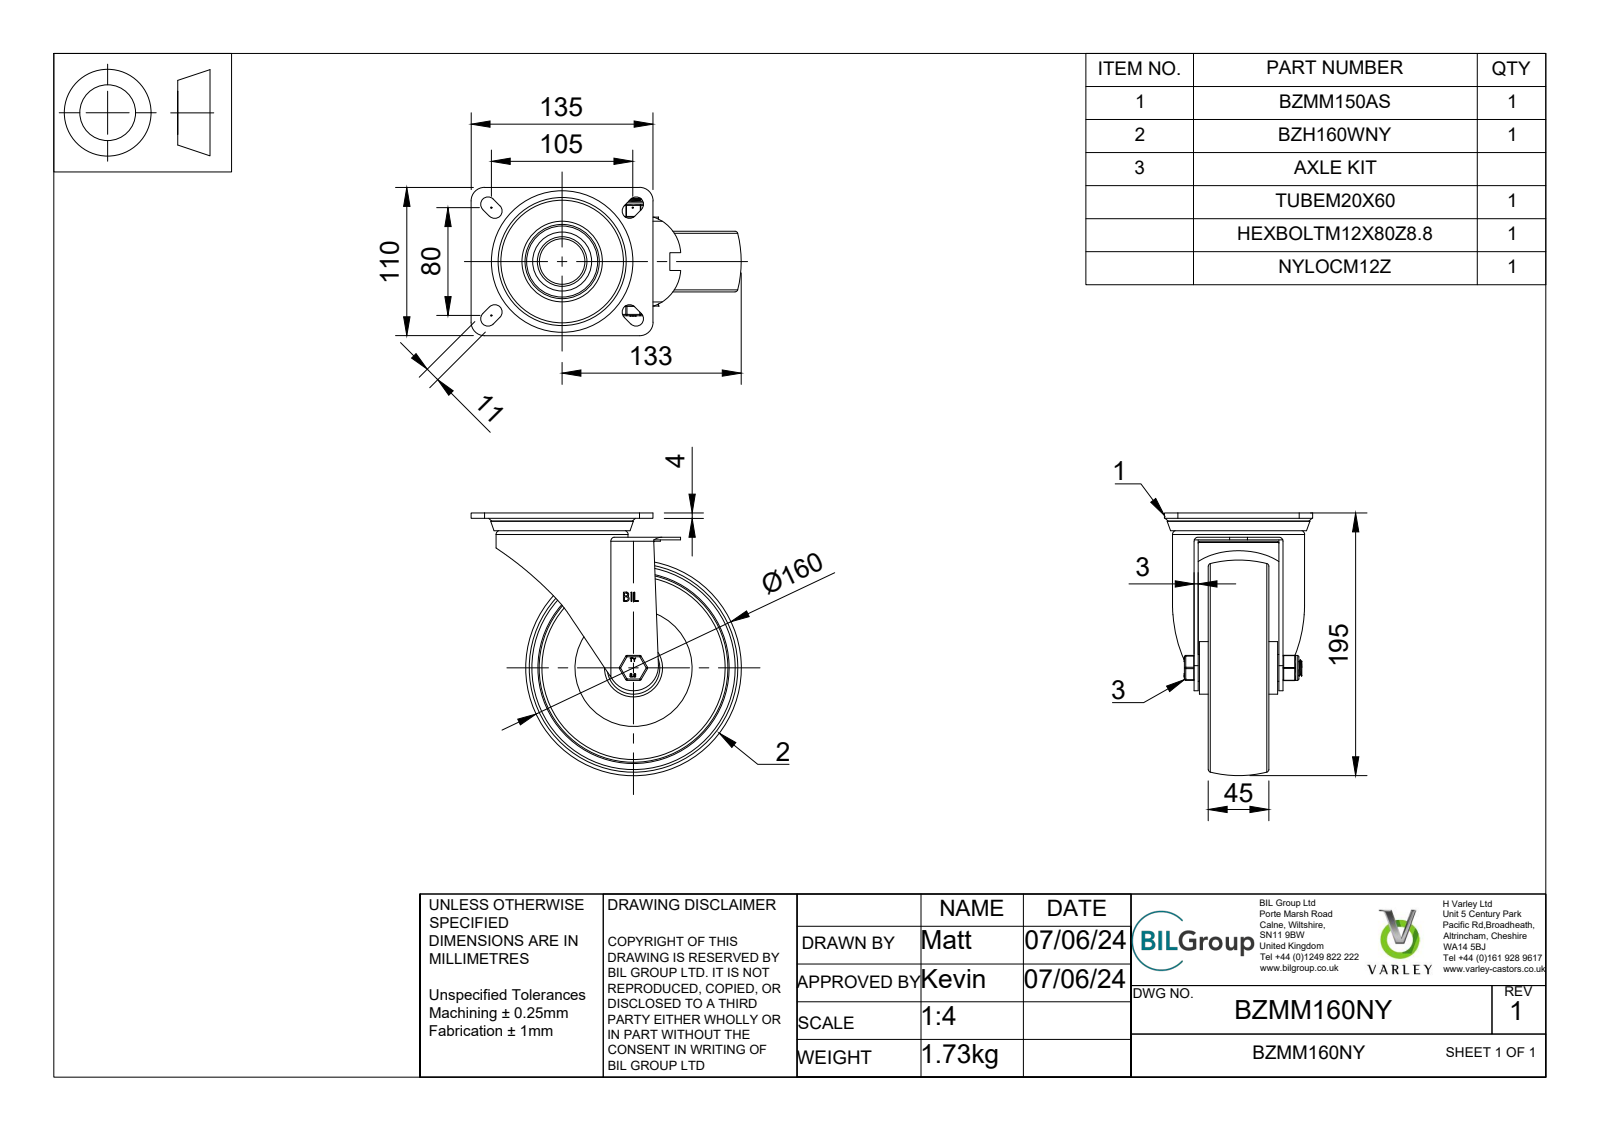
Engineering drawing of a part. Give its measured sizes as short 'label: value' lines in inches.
name: BZMM160NY v4; BZMM150AS - 2 v3; ZINC PLATED, PRESSED STEEL TOP PLATE; ZINC PLATED, PRESSED STEEL TOP PLATE Geometry (+7 more)
written by: Autodesk Translation Framework v13.14.0.145 (AUTOMOTIVE_DESIGN)
unit: in
bodies: 48 solids, 389 faces (127 planar, 119 cylindrical, 143 other)
size: 7.894 × 7.677 × 4.331
volume: 33.35 in³; area: 314.2 in²
holes: 1× ⌀0.472, 1× ⌀0.48, 1× ⌀0.492, 1× ⌀0.551, 1× ⌀0.807, 1× ⌀1.329, 1× ⌀1.565, 1× ⌀3.622, 1× ⌀5.512
bosses: 1× ⌀3.858, 1× ⌀3.071, 1× ⌀1.969, 1× ⌀1.535, 1× ⌀0.783, 1× ⌀0.728, 1× ⌀0.709, 1× ⌀0.466
rounds: 18× R0.02, 12× R0.039, 8× R0.217, 4× R0.059, 4× R0.394, 2× R0.118, 2× R1.18, 1× R0.732
face distances: 0.118, 0.276, 0.354, 0.157, 0.197, 1.161, 1.437, 2.48, 1.043, 1.319
